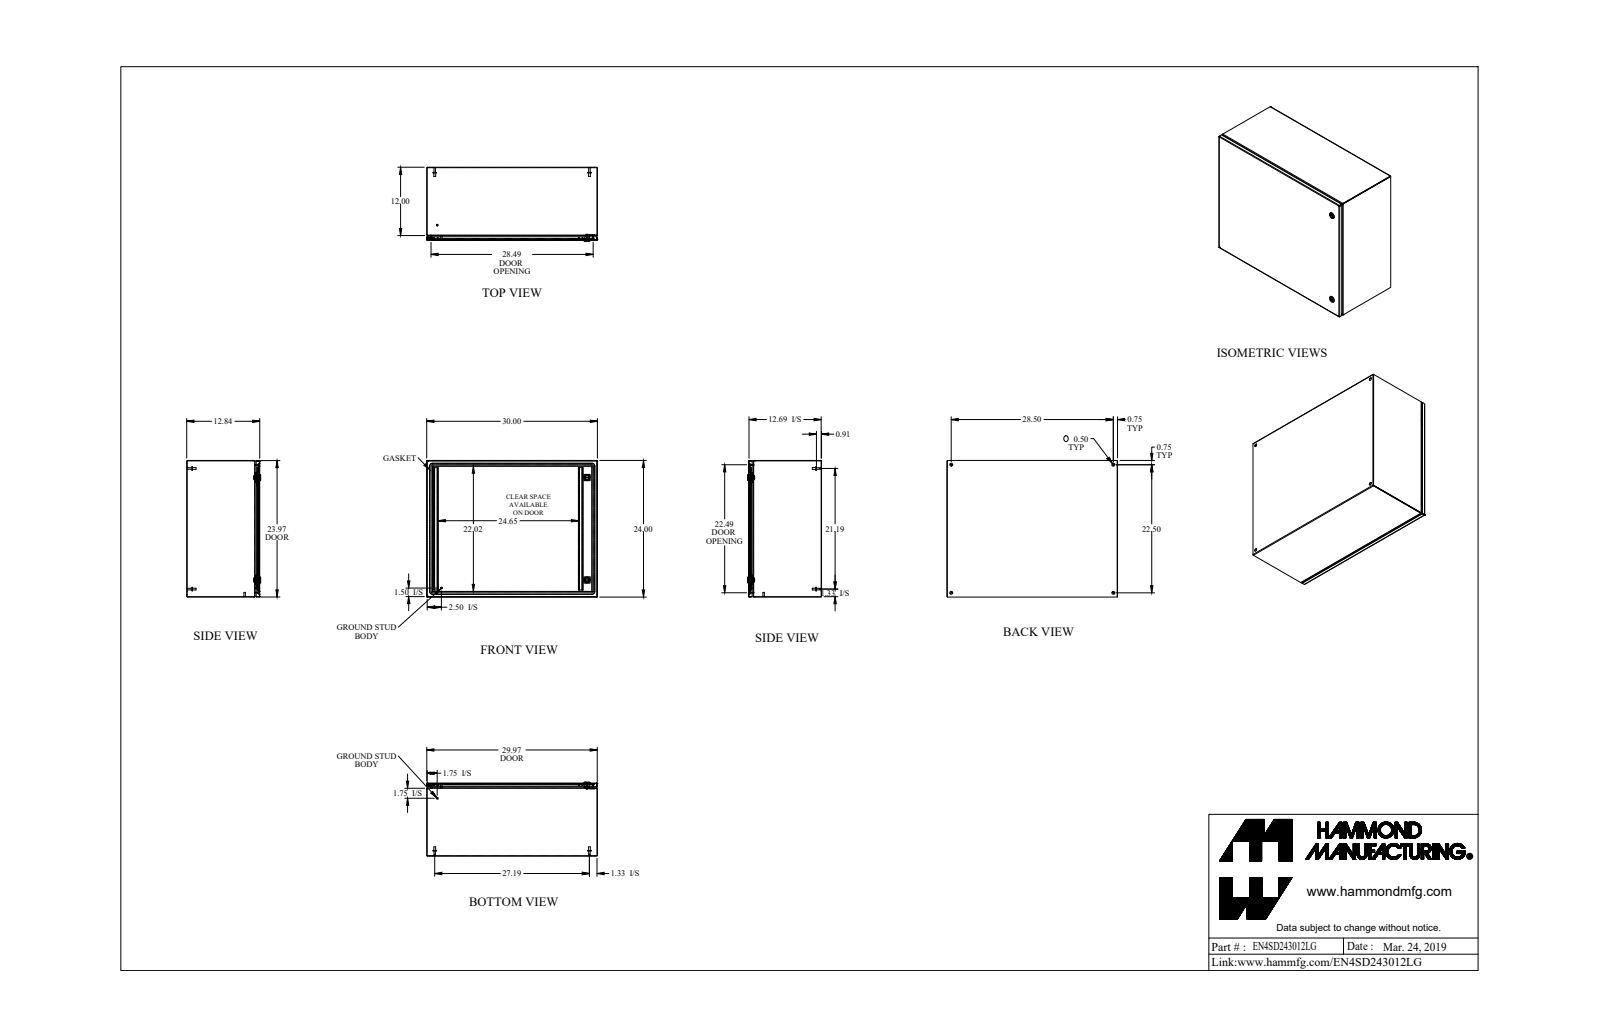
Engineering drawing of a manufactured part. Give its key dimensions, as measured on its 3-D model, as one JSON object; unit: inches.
{"part_name": "EN4SD243012LG", "step_written_by": "SolidWorks 2019 (AUTOMOTIVE_DESIGN)", "units": "inches", "bodies": {"solids": 29, "faces": 735, "planar": 363, "cylindrical": 245, "other": 127}, "overall_size": [30, 24, 12.997], "volume_in3": 225.1, "surface_area_in2": 6296, "round_holes": [[0.5, 4], [0.232, 2], [0.625, 2], [0.785, 2], [0.172, 1], [0.24, 1], [0.242, 1]], "round_bosses_or_shafts": [[0.625, 4], [0.313, 4], [0.27, 4], [1.1, 2], [0.525, 2], [0.281, 2], [0.25, 2], [0.455, 1]], "partial_cylinders_radius": [[0.036, 14], [0.108, 14], [0.043, 12], [0.081, 12], [0.312, 12], [0.1, 8], [0.006, 4], [0.062, 4]], "face_to_face_distances": [0.072, 12.765, 12.693, 12.837, 23.928, 29.928, 23.856, 24, 29.856, 30], "hole_center_spacings": [22.5, 27.519, 28.5, 36.311, 2.493, 2.494, 17.999, 20.277]}
